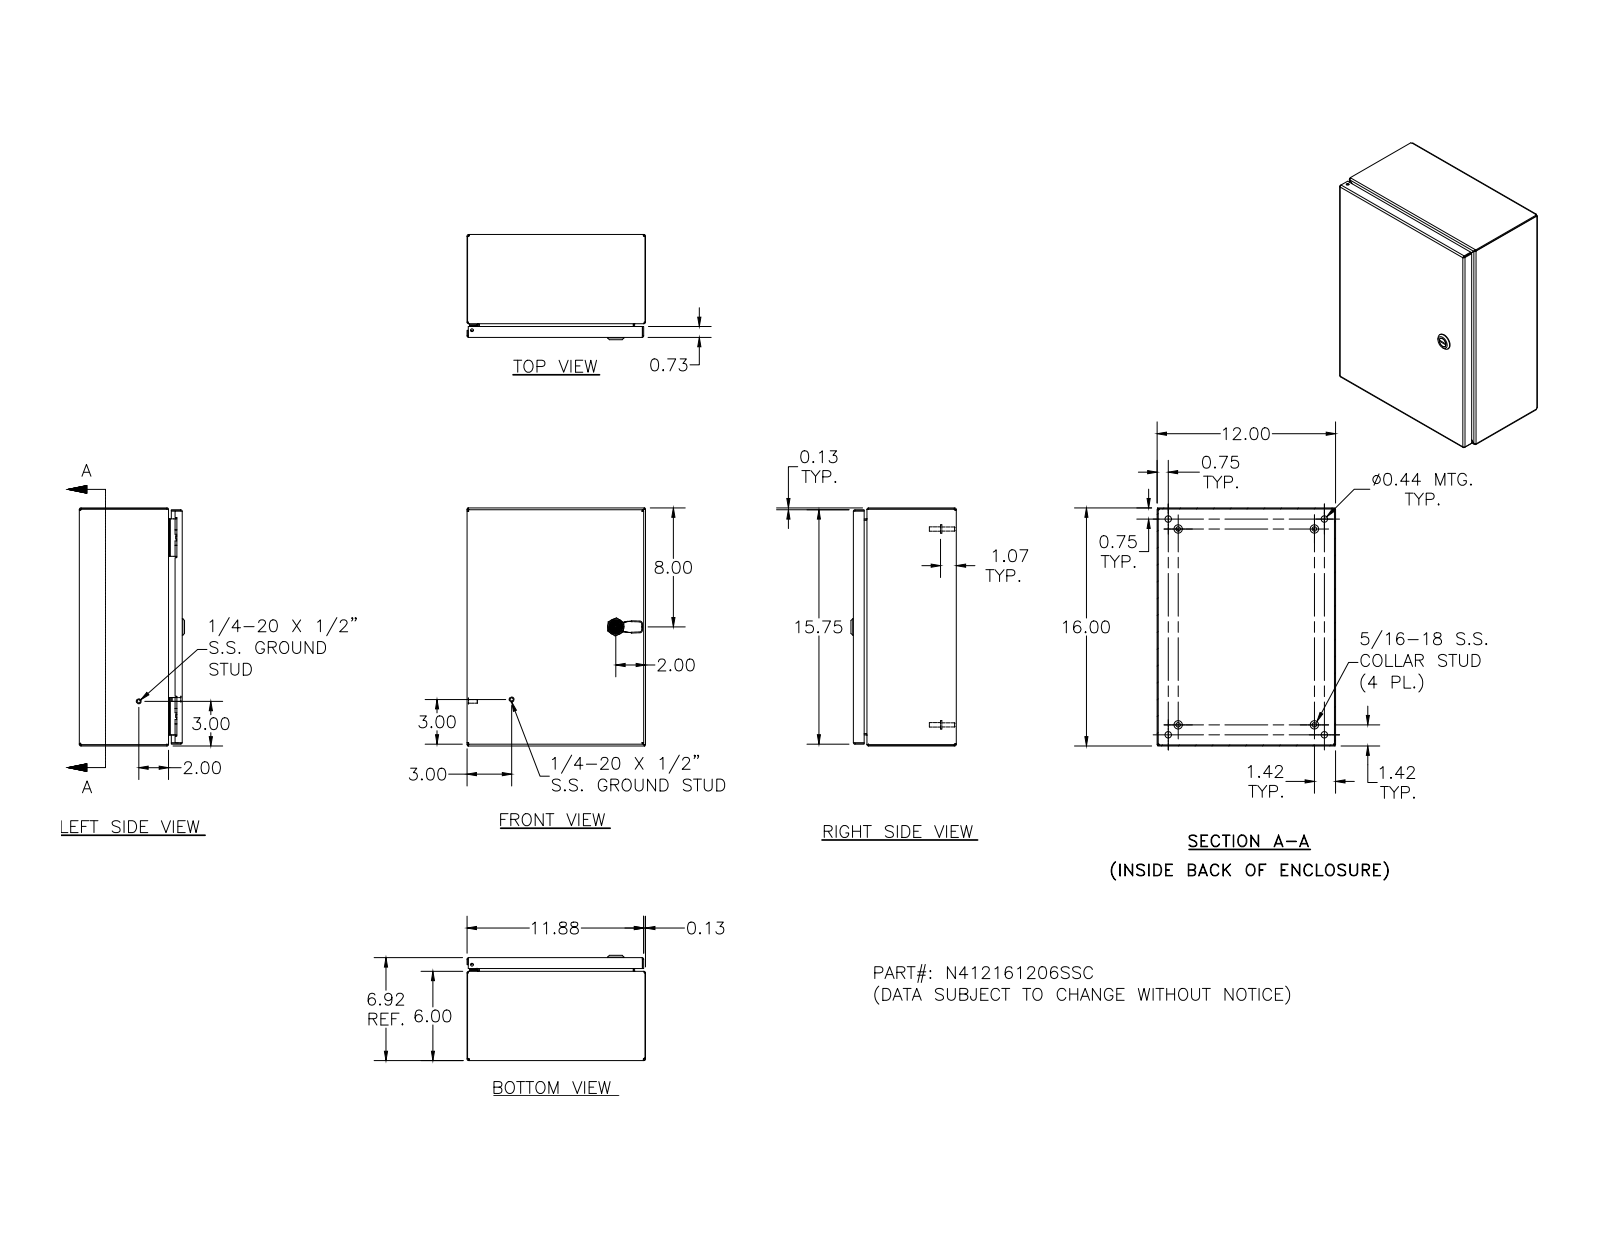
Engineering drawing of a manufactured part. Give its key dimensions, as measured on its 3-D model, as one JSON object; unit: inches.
{"part_name": "N412161206SSC; N412161206SSCBKP; 388151; N4121612SSCLID (+8 more)", "step_written_by": "Autodesk Inventor 2011 (AUTOMOTIVE_DESIGN)", "units": "inches", "bodies": {"solids": 34, "faces": 1384, "planar": 531, "cylindrical": 509, "other": 344}, "overall_size": [16, 12, 7.075], "volume_in3": 62.27, "surface_area_in2": 1697, "round_holes": [[0.188, 5], [0.093, 4], [0.152, 4], [0.167, 4], [0.172, 4], [0.437, 4], [0.156, 2], [0.187, 1], [0.197, 1], [0.315, 1], [0.394, 1], [0.402, 1]], "round_bosses_or_shafts": [[0.25, 10], [0.563, 4], [0.36, 4], [0.32, 4], [0.3, 4], [0.275, 4], [0.256, 4], [0.164, 4]], "partial_cylinders_radius": [[0.031, 30], [0.05, 26], [0.105, 20], [0.016, 18], [0.125, 14], [0.02, 9], [0.032, 8], [0.07, 8]], "face_to_face_distances": [0.074, 6.843, 11.926, 6.769, 6.917, 15.926, 12, 11.852, 16, 15.852], "hole_center_spacings": [12, 0.017, 0.66, 0.019, 0.5, 0.648, 0.652, 0.656]}
